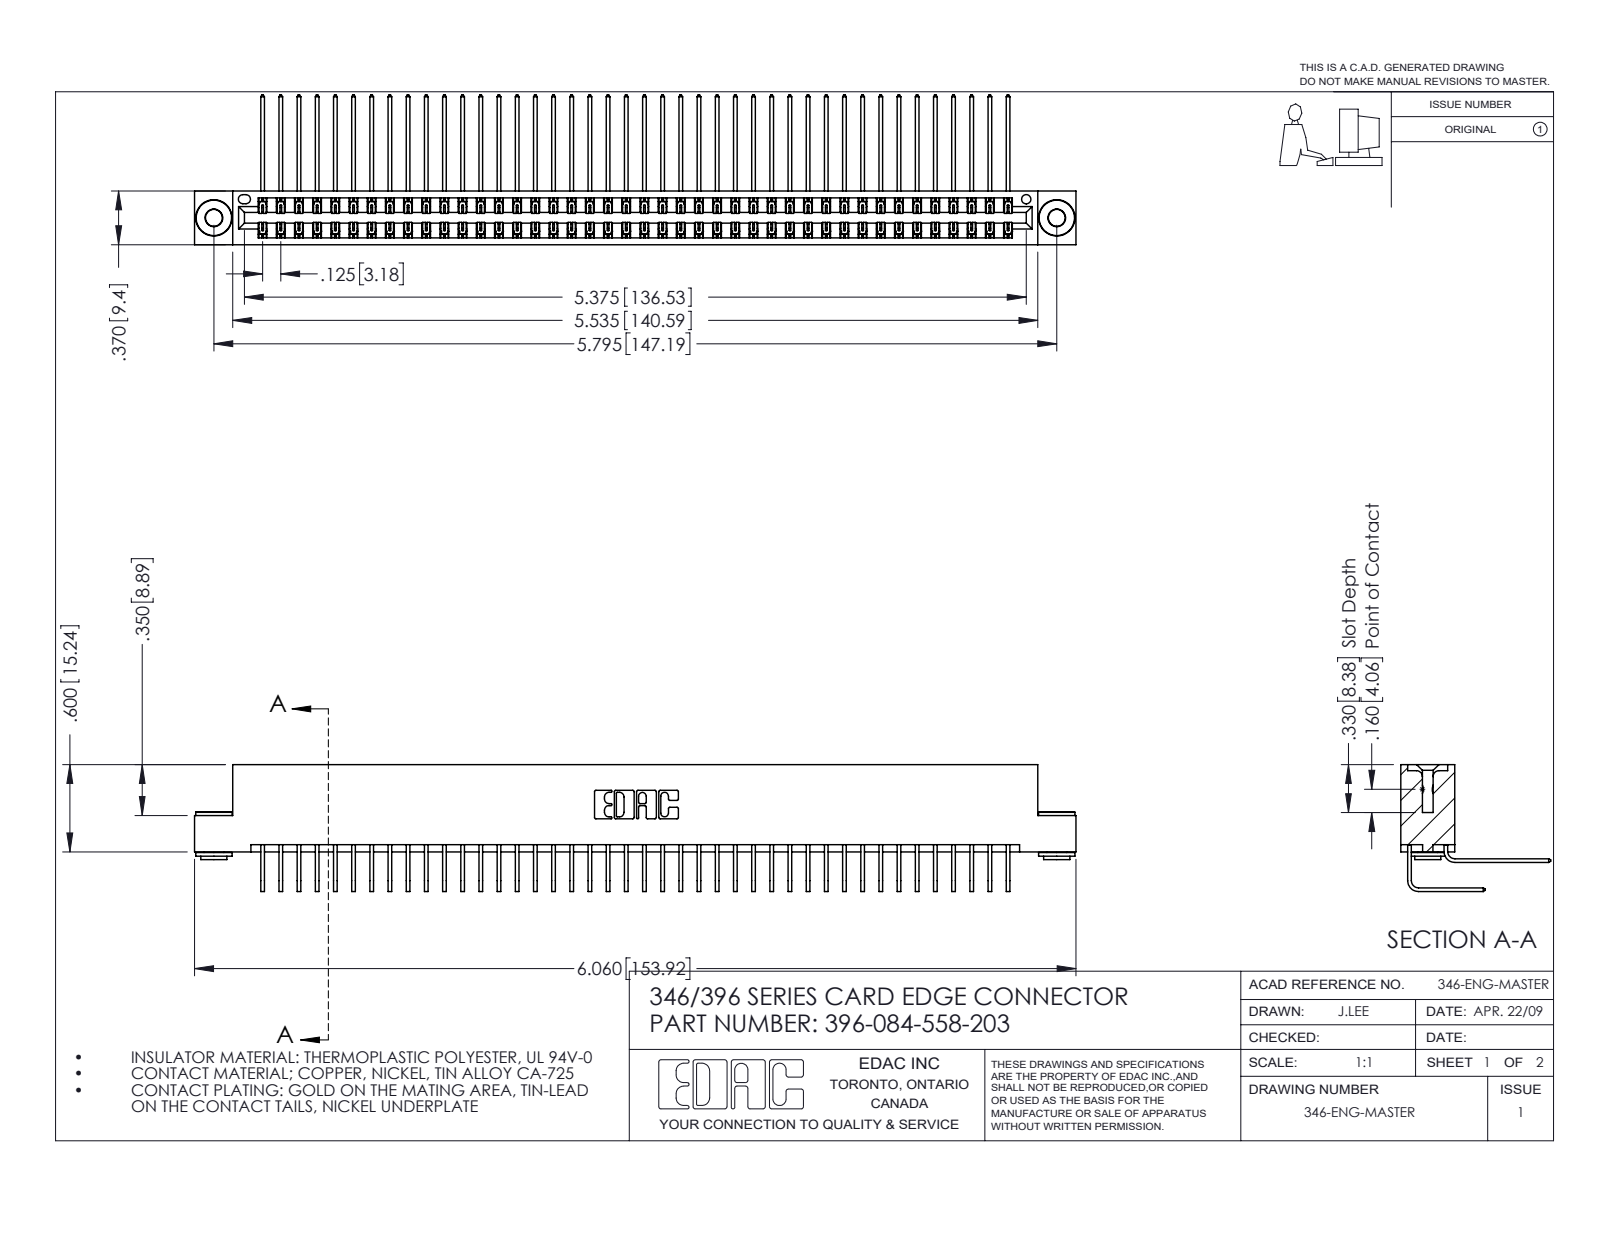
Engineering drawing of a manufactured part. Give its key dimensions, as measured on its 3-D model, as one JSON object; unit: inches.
{"part_name": "346 Part_Flush Mounting Lugs - 0.156 Dia-TH; 345-250-002_345-250-002-102; 396-084-558-203; 345-292-001_558 Tail - 2 (+1 more)", "step_written_by": "SolidWorks 2016 (CONFIG_CONTROL_DESIGN)", "units": "inches", "bodies": {"solids": 87, "faces": 4696, "planar": 3194, "cylindrical": 1494, "other": 8}, "overall_size": [6.06, 1.03, 0.873], "volume_in3": 0.947, "surface_area_in2": 36.99, "round_holes": [[0.116, 2], [0.156, 2], [0.064, 1]], "round_bosses_or_shafts": [[0.25, 2], [0.18, 2], [0.136, 2]], "partial_cylinders_radius": [[0.006, 126], [0.01, 22], [0.007, 6], [0.031, 6], [0.026, 3], [0.014, 2], [0.022, 2], [0.024, 2]], "face_to_face_distances": [0.322, 0.048, 0.025, 0.25, 0.37, 0.298, 0.072, 0.275, 0.148, 0.222], "hole_center_spacings": [0.246, 5.586, 5.795]}
